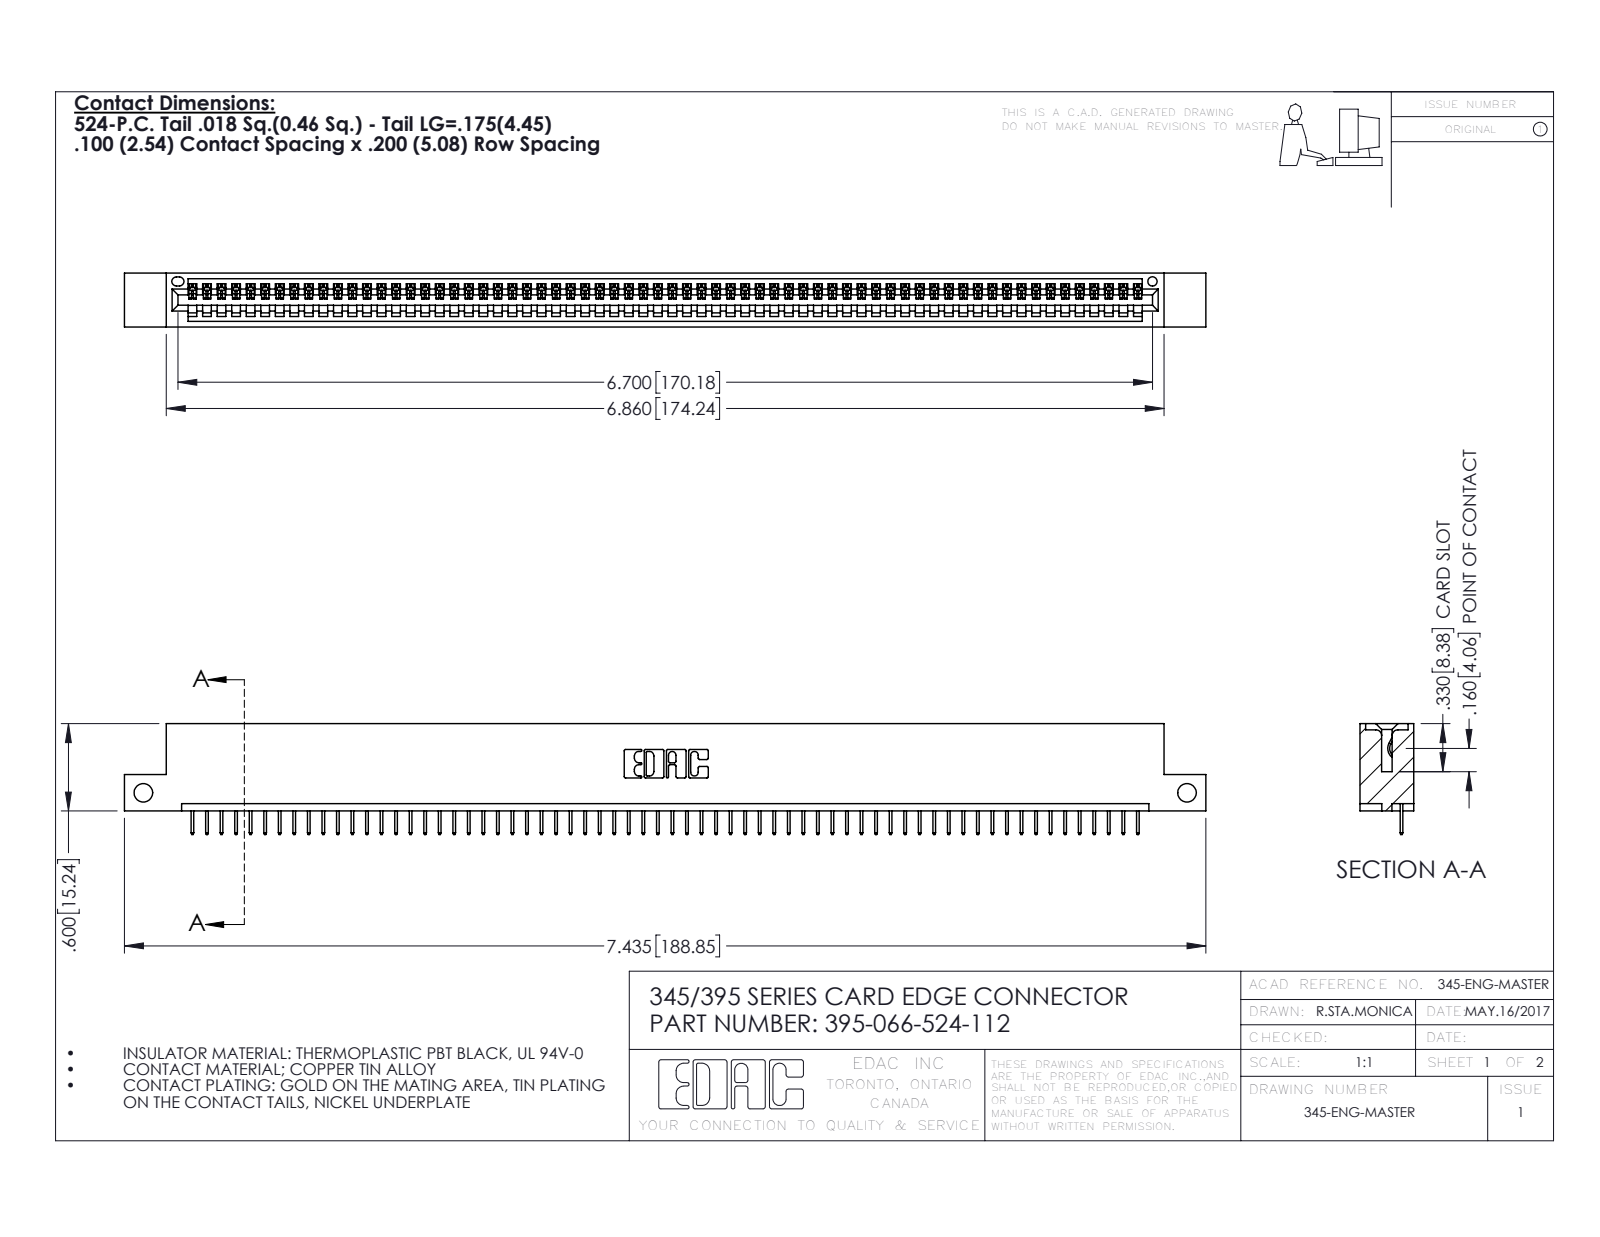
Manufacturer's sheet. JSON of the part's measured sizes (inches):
{"part_name": "395-066-524-112; 345-292-001_345-293-124; 345 Part_Flush Mounting Lugs - Side Mount", "step_written_by": "SolidWorks 2016 (CONFIG_CONTROL_DESIGN)", "units": "inches", "bodies": {"solids": 67, "faces": 4218, "planar": 3116, "cylindrical": 1102, "other": 0}, "overall_size": [7.435, 0.762, 0.37], "volume_in3": 1.085, "surface_area_in2": 35.63, "round_holes": [[0.128, 2], [0.064, 1]], "partial_cylinders_radius": [[0.006, 132], [0.01, 22], [0.007, 6], [0.031, 6], [0.026, 3], [0.031, 2], [0.04, 2], [0.014, 1]], "face_to_face_distances": [0.072, 0.298, 0.37, 0.2, 0.098, 0.272, 0.025, 0.225, 0.072, 0.149], "hole_center_spacings": [7.175]}
